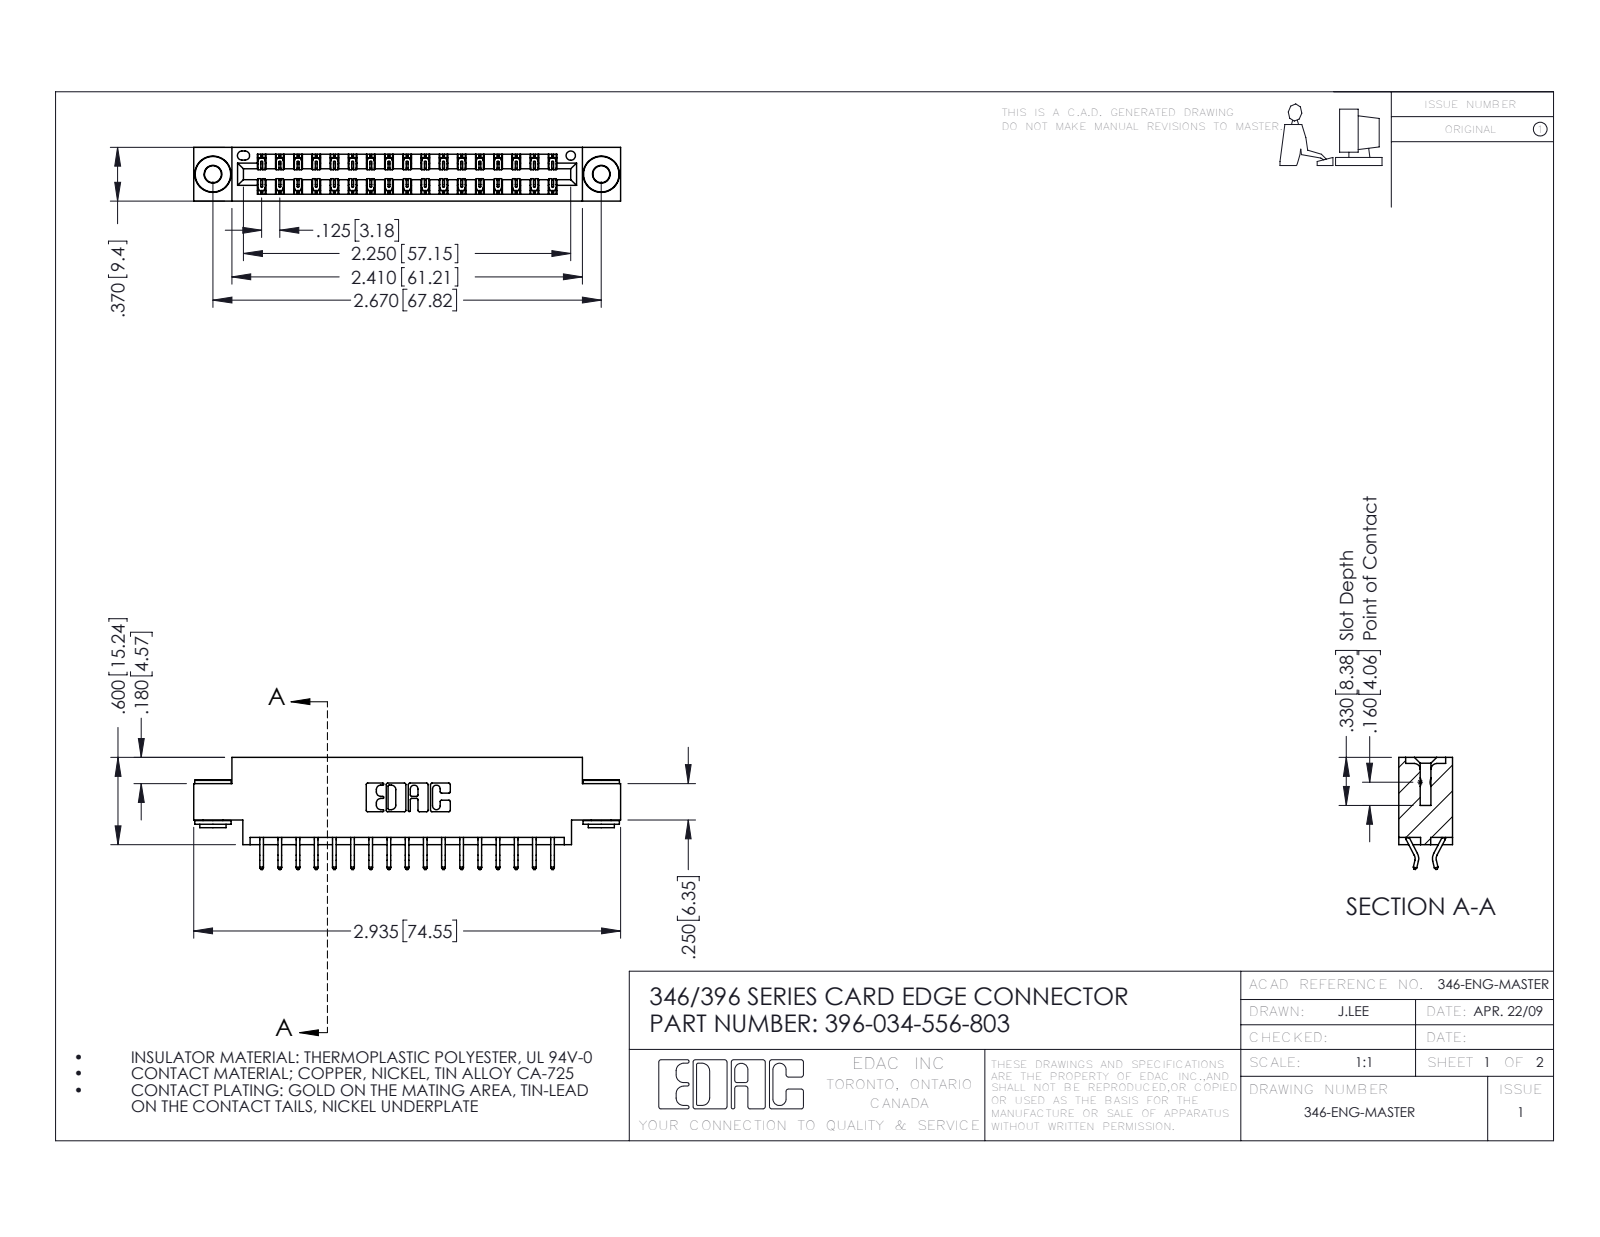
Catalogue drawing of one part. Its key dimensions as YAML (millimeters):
part_name: "346 Part_0.170 Offset - 0.156 Dia-TH; 345-292-001_556 Tail; 345-250-002_345-250-002-102; 396-034-556-803"
step_written_by: "SolidWorks 2016 (CONFIG_CONTROL_DESIGN)"
units: millimeters
bodies: {solids: 37, faces: 2136, planar: 1416, cylindrical: 712, other: 8}
overall_size: [74.5, 19.6, 9.4]
volume: 6930
surface_area: 9510
round_holes:
  - {diameter: 2.9, count: 2}
  - {diameter: 4, count: 2}
  - {diameter: 1.6, count: 1}
round_bosses_or_shafts:
  - {diameter: 6.4, count: 2}
  - {diameter: 4.6, count: 2}
  - {diameter: 3.5, count: 2}
partial_cylinders:
  - {radius: 0.2, count: 51}
  - {radius: 0.3, count: 22}
  - {radius: 0.2, count: 6}
  - {radius: 0.8, count: 6}
  - {radius: 0.7, count: 3}
  - {radius: 0.3, count: 2}
  - {radius: 0.4, count: 2}
  - {radius: 0.6, count: 2}
face_to_face_distances: [1.2, 8.2, 9.4, 6.4, 0.6, 7, 1.8, 7.6, 3.8, 5.6]
hole_center_spacings: [6.2, 62.6, 67.8]
